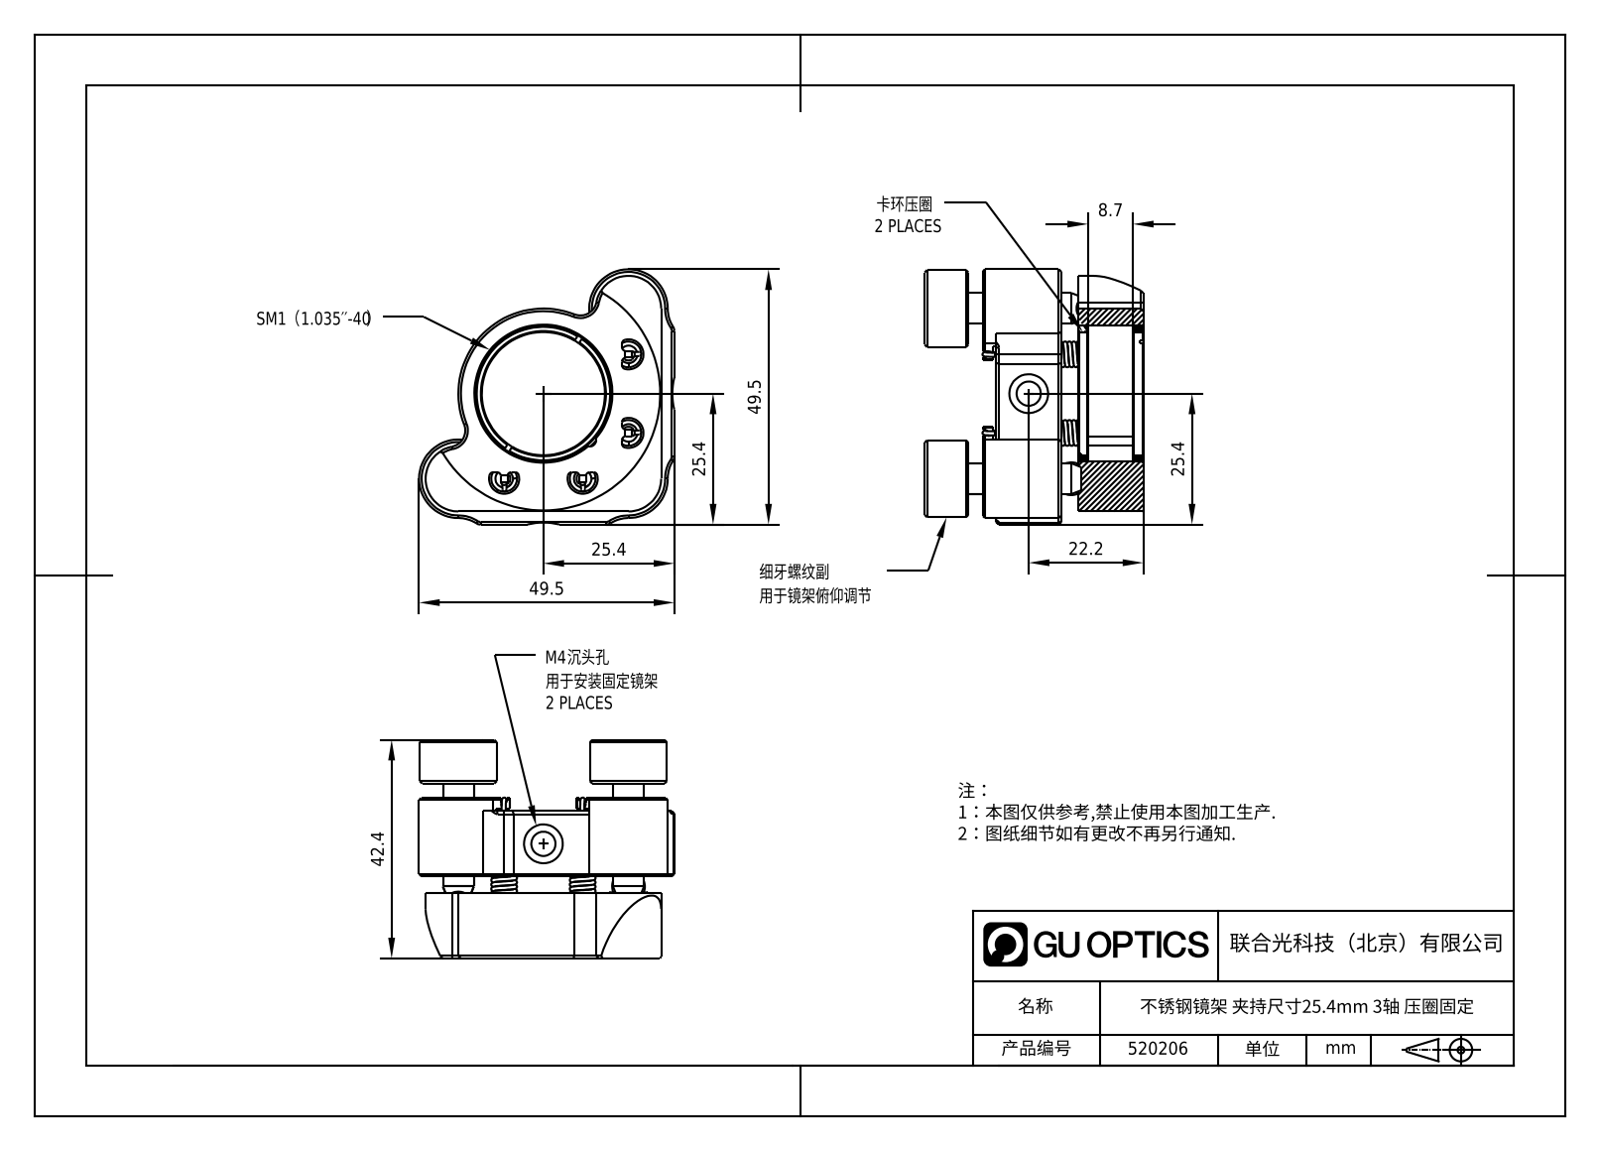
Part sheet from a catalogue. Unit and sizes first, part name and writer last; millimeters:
Units: millimetres
Overall size (bounding box): 49.53 × 49.53 × 42.7
Round holes (diameter × count): ⌀6.35 ×7, ⌀3.99 ×3, ⌀4 ×3, ⌀6 ×3, ⌀7 ×3, ⌀2.01 ×2, ⌀4.7 ×2, ⌀7.54 ×2, ⌀23.89 ×1
Round bosses / shafts (diameter × count): ⌀4 ×6, ⌀15 ×3, ⌀15.24 ×2, ⌀26.29 ×1
Partial cylindrical surfaces — rounded edges, fillets, slot ends (radius × count): R0.79 ×16, R6.48 ×14, R0.64 ×8, R1 ×4, R1.93 ×4, R2.92 ×4, R6.35 ×3, R1.59 ×2
Main face-to-face distances: 12.7, 15.87, 2.54, 3.17, 15.24, 31.11, 18.41, 28.57, 8.5, 13.84
Hole centre spacings: 8.89, 18.18, 24.13, 23.35, 5, 15.24, 25.72, 33.02
Volume: 28 531 mm³ · Surface area: 20 489 mm²
Bodies: 23 solids, 634 faces (204 planar, 175 cylindrical, 255 other)
Part name (STEP PRODUCT): 替代进口不锈钢光学调整架前面板，卡圈固定式_1.1.20.13.1_ZJO-SM1.0; ZFK不锈钢透镜卡环压圈_1.8.9.2_ZFKS-K1.0; DXS-0625标准型六角调节器 _3.2.2.16.1-DXS-0625-26.6; DXG，平面螺纹旋钮_3.2.10.19-DXG-M0625-15-8.5S (+3 more)
STEP written by: SolidWorks 2021 (CONFIG_CONTROL_DESIGN)
